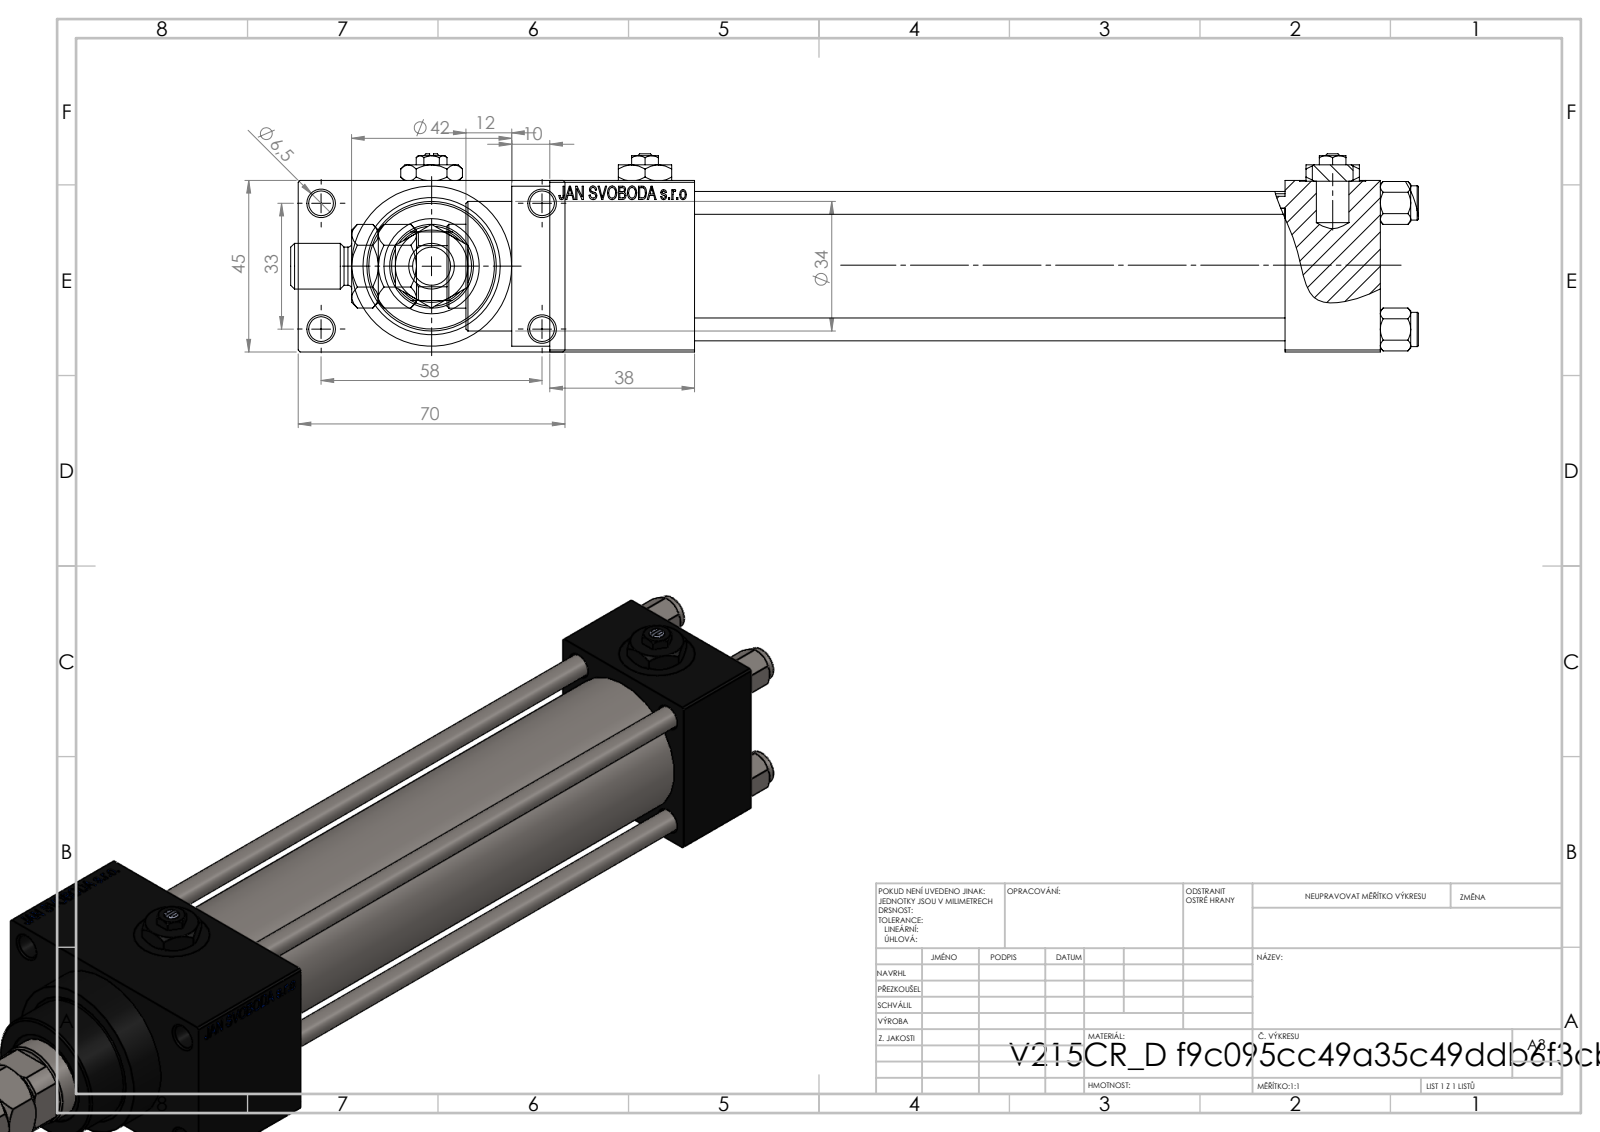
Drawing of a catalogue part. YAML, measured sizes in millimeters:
part_name: "MTA; Zatka_pro_OIL_PORT; V215CR_VCP_D; V215_VC_A (+3 more)"
step_written_by: "SolidWorks 2019 (CONFIG_CONTROL_DESIGN)"
units: millimeters
bodies: {solids: 14, faces: 1252, planar: 557, cylindrical: 103, other: 592}
overall_size: [296, 70, 52]
volume: 335025
surface_area: 122206
round_holes:
  - {diameter: 6, count: 4}
  - {diameter: 6.5, count: 4}
  - {diameter: 13.16, count: 4}
  - {diameter: 20, count: 4}
  - {diameter: 7, count: 3}
  - {diameter: 10.5, count: 1}
  - {diameter: 22, count: 1}
  - {diameter: 24, count: 1}
  - {diameter: 25, count: 1}
  - {diameter: 32, count: 1}
  - {diameter: 33, count: 1}
round_bosses_or_shafts:
  - {diameter: 9, count: 4}
  - {diameter: 42, count: 1}
  - {diameter: 38, count: 1}
  - {diameter: 34, count: 1}
  - {diameter: 12, count: 1}
  - {diameter: 10, count: 1}
partial_cylinders:
  - {radius: 10.5, count: 1}
face_to_face_distances: [45, 25, 12.5, 155, 180, 57.5, 193, 38, 218, 70]
hole_center_spacings: [12.4, 23.48, 33.2, 33.37, 35.35, 45.6, 56.35, 33]
